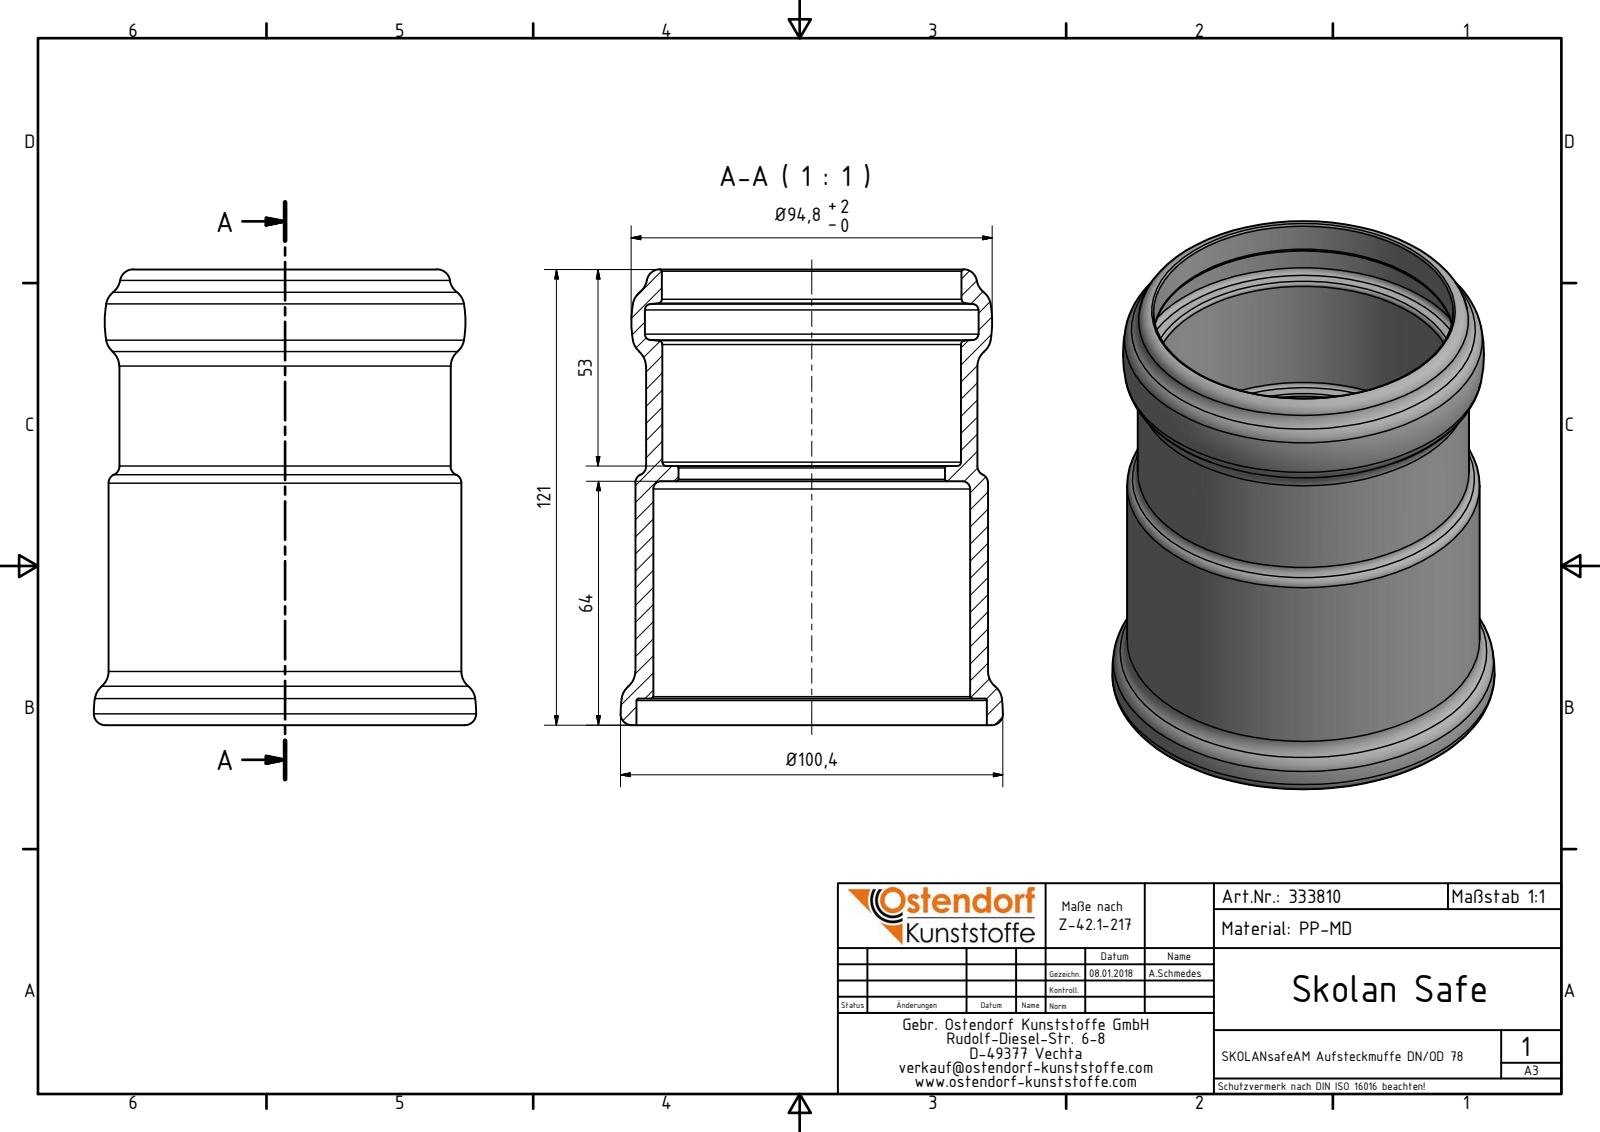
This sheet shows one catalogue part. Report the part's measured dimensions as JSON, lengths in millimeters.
{"part_name": "333810 SKOLANsafeAM Aufsteckmuffe DN_OD 78", "step_written_by": "Autodesk Inventor 2016 (AUTOMOTIVE_DESIGN)", "units": "millimeters", "bodies": {"solids": 1, "faces": 37, "planar": 4, "cylindrical": 8, "other": 25}, "overall_size": [119.6, 100.4, 100.4], "volume_mm3": 156934, "surface_area_mm2": 72886, "round_holes": [[70, 1], [78.4, 1], [78.7, 1], [83.2, 1], [87.6, 1], [92, 1]], "round_bosses_or_shafts": [[92.6, 1], [87, 1]], "face_to_face_distances": [57, 61, 4, 7, 64, 68]}
